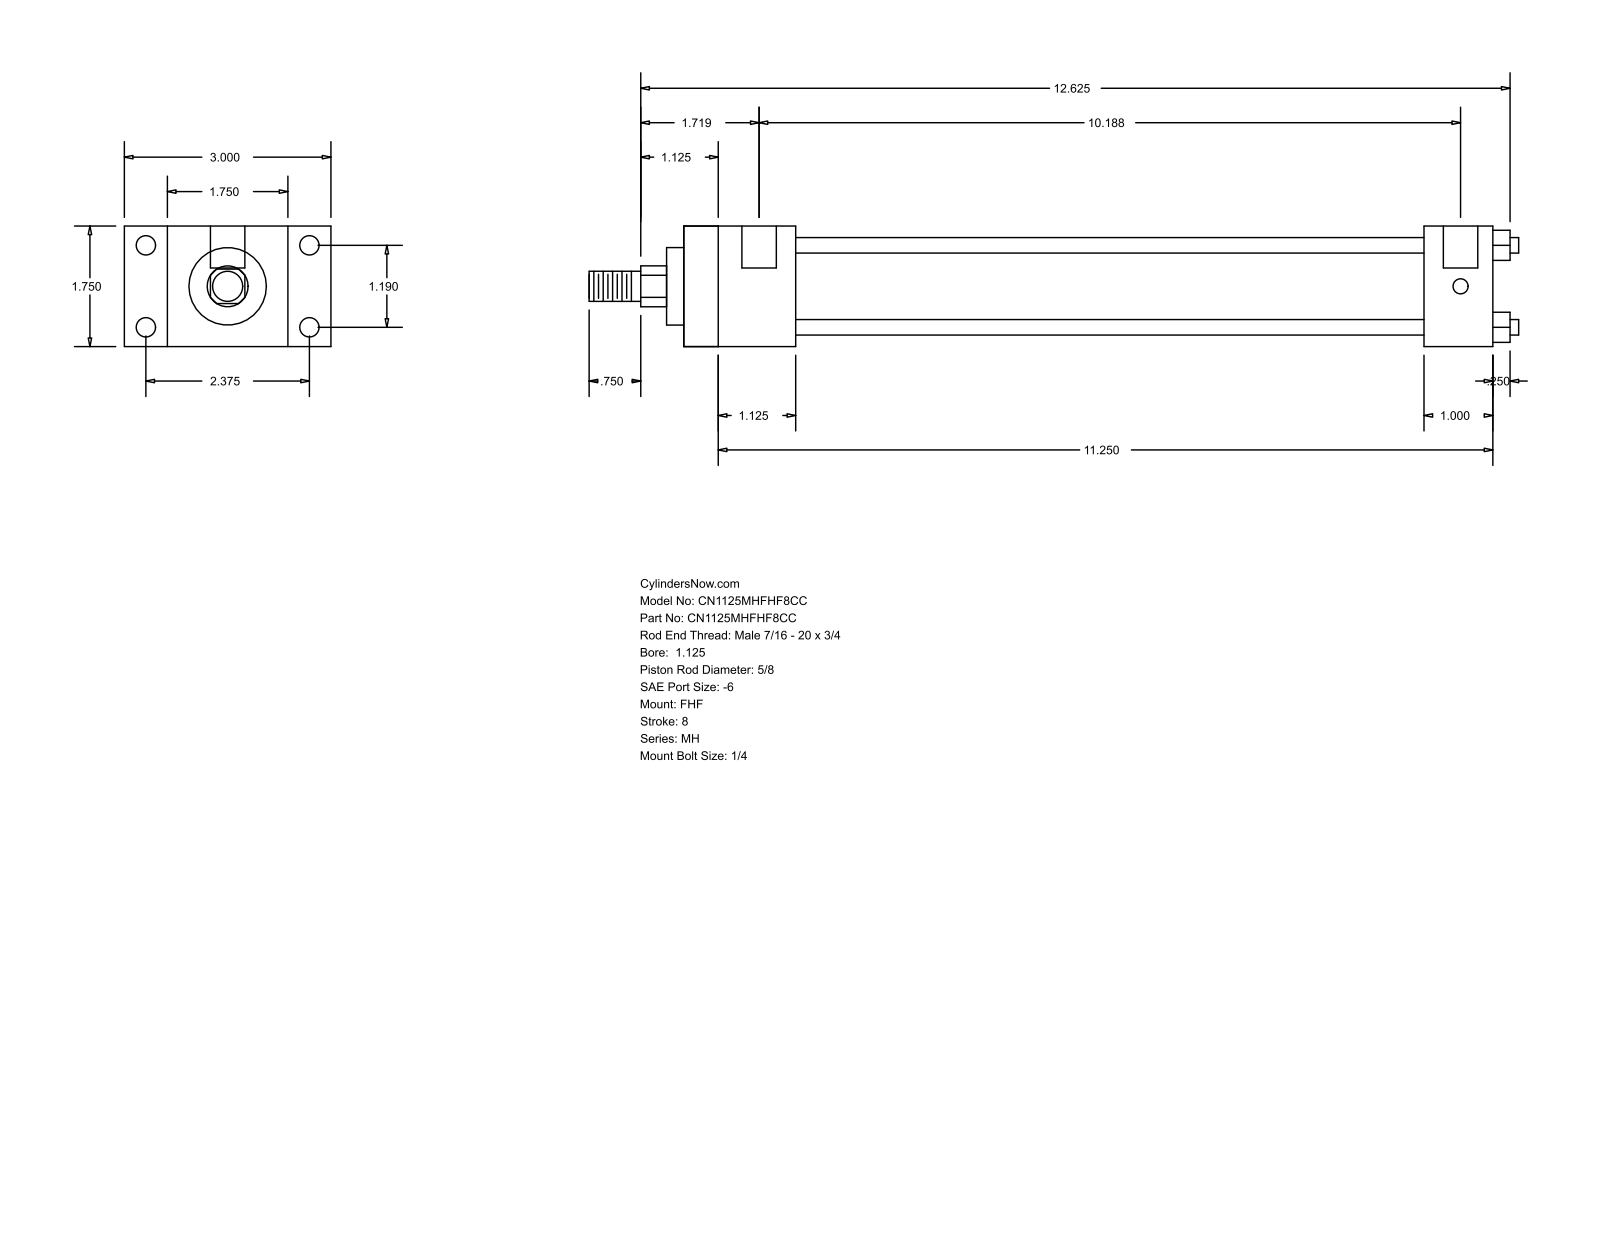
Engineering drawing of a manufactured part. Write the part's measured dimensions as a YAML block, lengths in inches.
part_name: "MH_FHF__0112_0.625"
step_written_by: "GSSL Pune (CONFIG_CONTROL_DESIGN)"
units: inches
bodies: {solids: 0, faces: 88, planar: 60, cylindrical: 28, other: 0}
overall_size: [13.5, 3, 1.75]
round_holes:
  - {diameter: 0.219, count: 4}
  - {diameter: 0.281, count: 4}
  - {diameter: 0.5, count: 2}
round_bosses_or_shafts:
  - {diameter: 0.225, count: 4}
  - {diameter: 1.375, count: 1}
  - {diameter: 1.125, count: 1}
  - {diameter: 0.625, count: 1}
  - {diameter: 0.437, count: 1}
partial_cylinders:
  - {radius: 0.297, count: 1}
face_to_face_distances: [1.75, 0.625, 2.375, 1.625, 3, 11.75, 10.125, 10.75, 9.125, 1]
hole_center_spacings: [1.19, 2.375, 2.656, 10.063, 0.125, 10.187]
